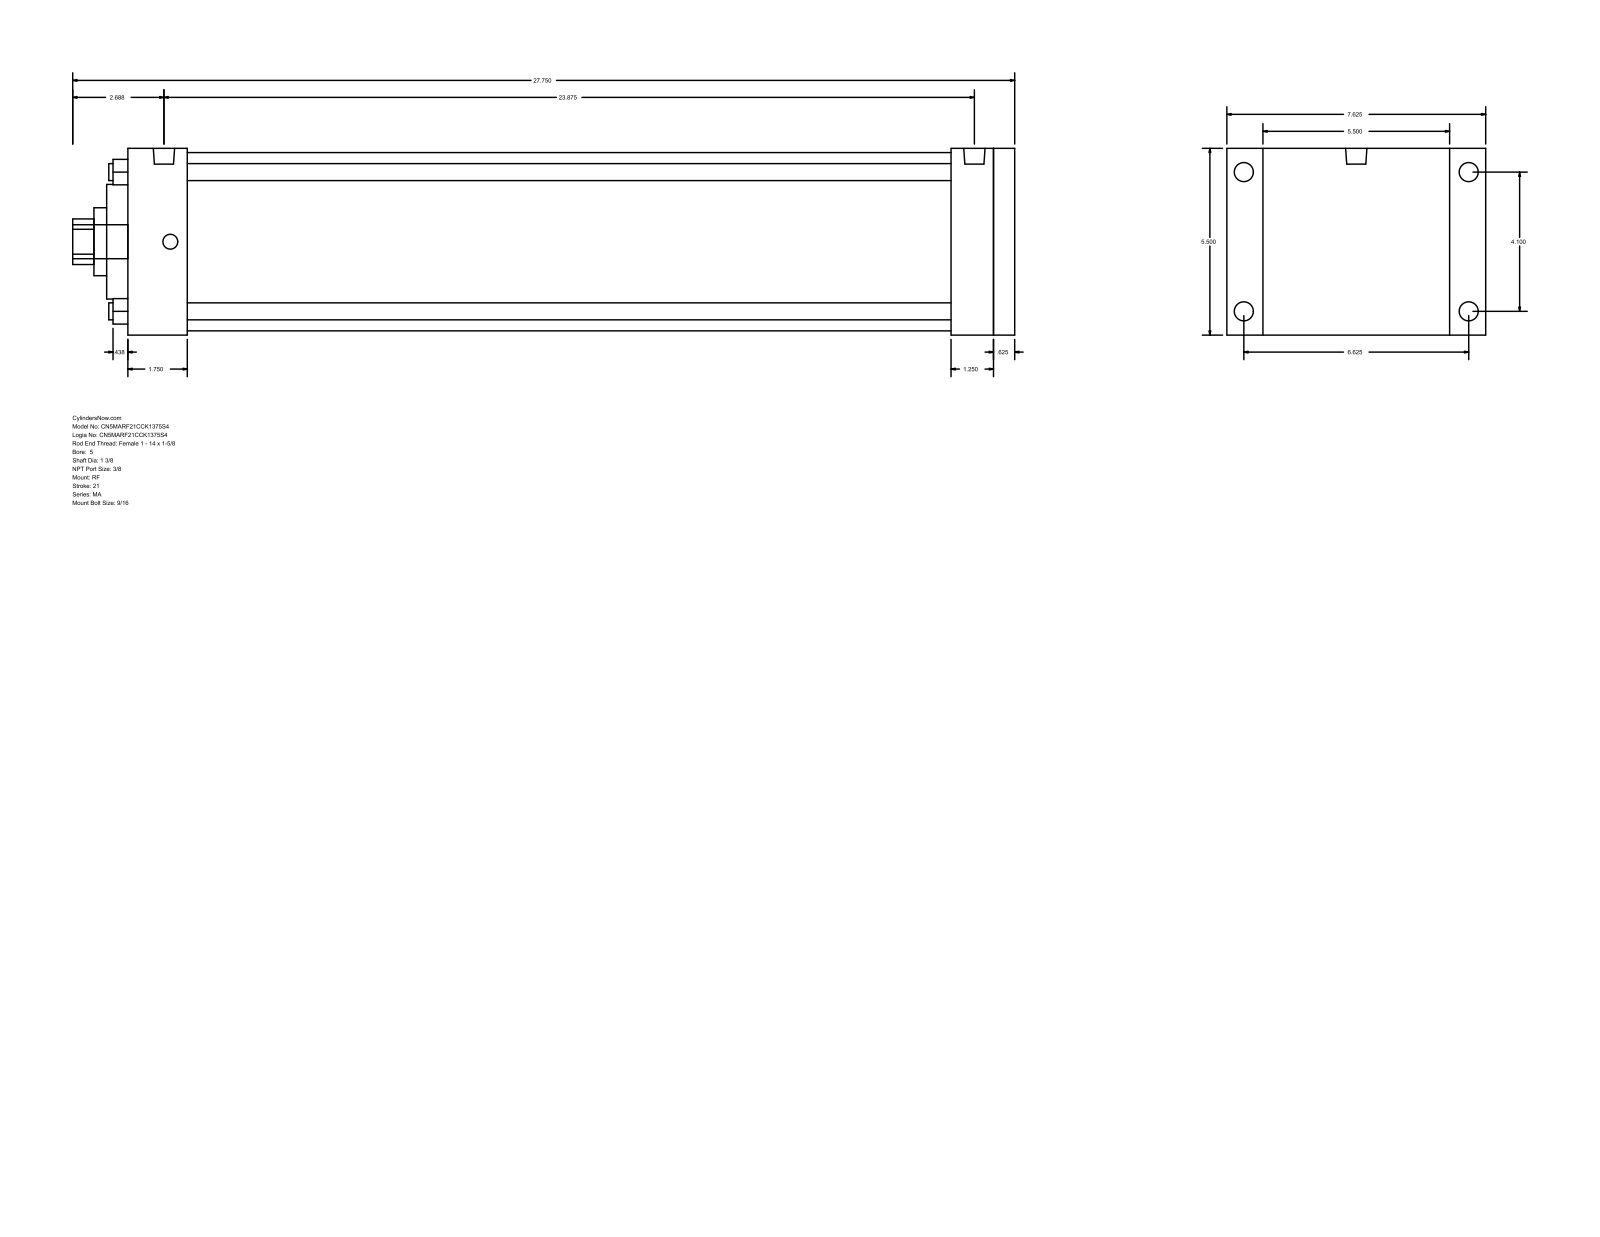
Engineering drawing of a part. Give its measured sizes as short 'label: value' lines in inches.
name: MA_RF__0500_1.375
written by: GSSL Pune (CONFIG_CONTROL_DESIGN)
unit: in
bodies: 0 solids, 94 faces (65 planar, 29 cylindrical, 0 other)
size: 27.75 × 7.625 × 5.5
holes: 4× ⌀0.5, 1× ⌀1.375, 1× ⌀2, 1× ⌀3.375, 1× ⌀5.25
bosses: 4× ⌀0.563, 4× ⌀0.437, 2× ⌀0.627, 1× ⌀1
rounds: 1× R0.672
face distances: 5.5, 26.125, 0.625, 25.5, 1.75, 23.75, 24.375, 24.25, 22.5, 1.25
hole spacings: 2.899, 4.1, 5.798
